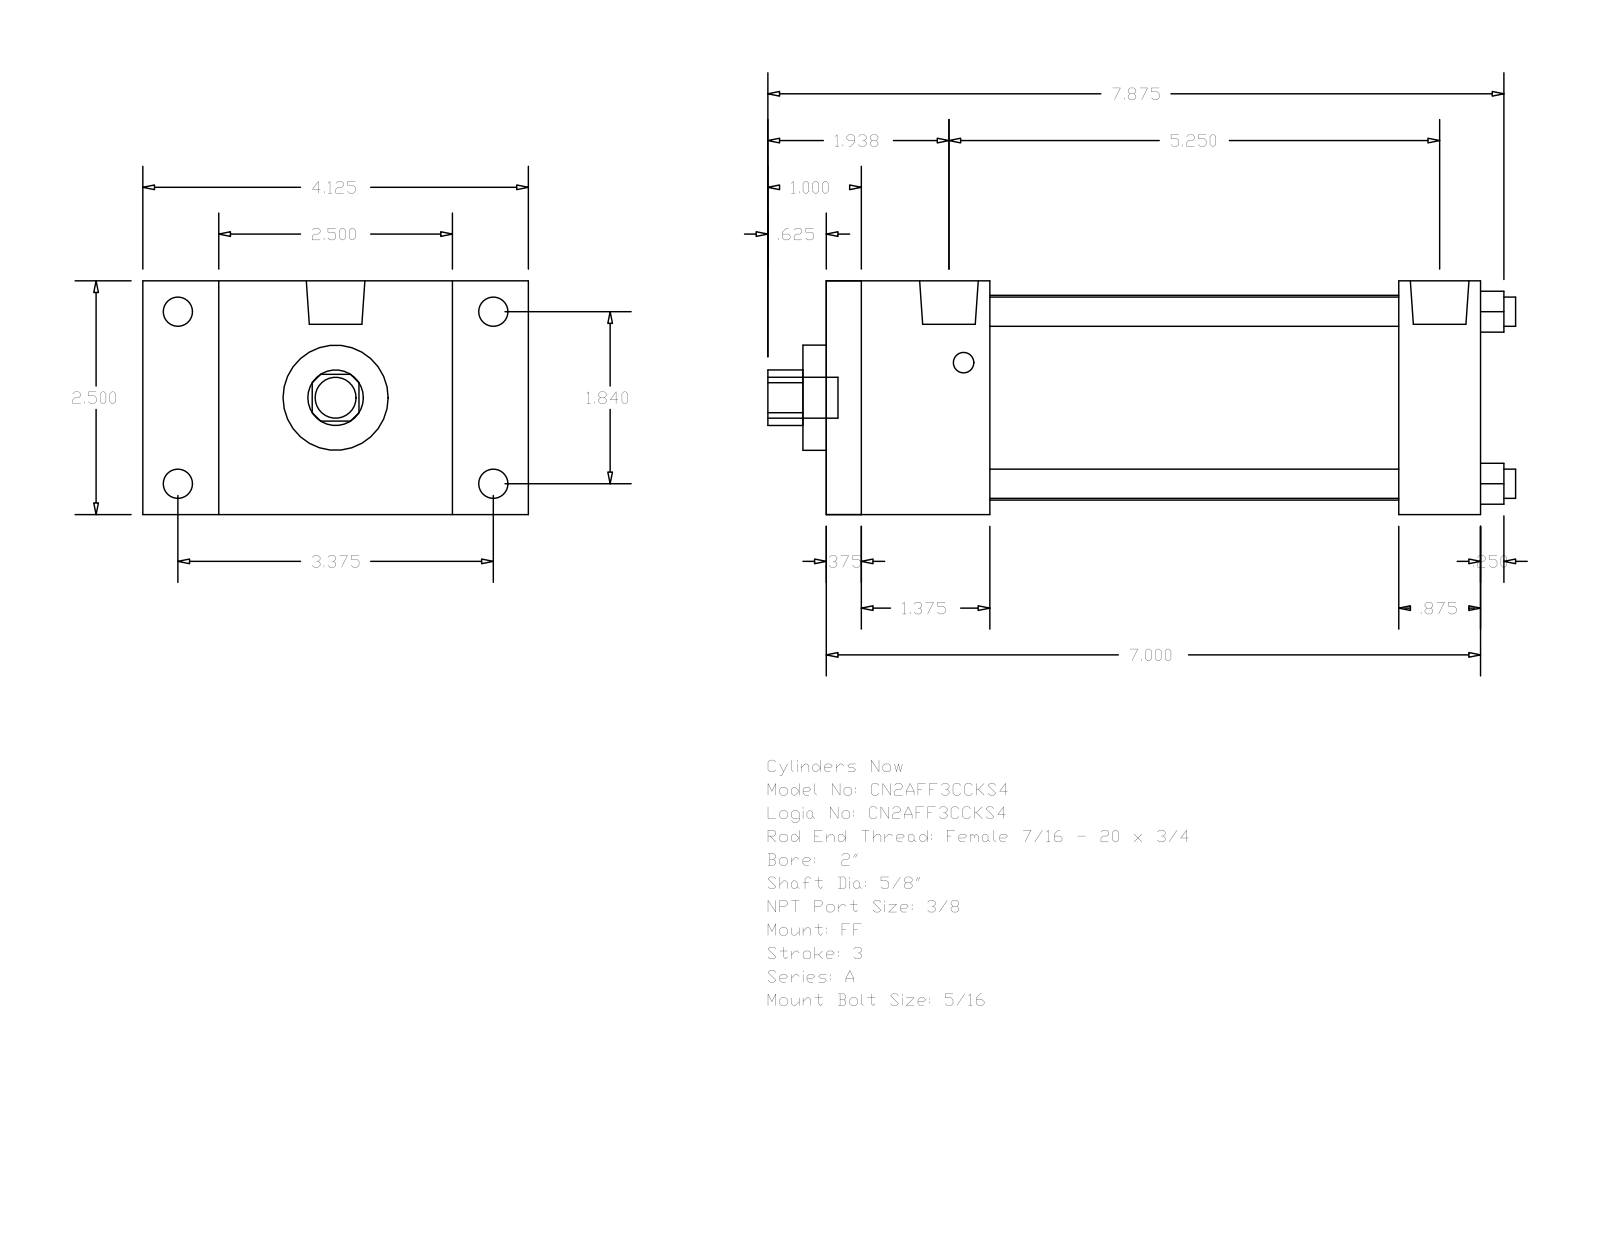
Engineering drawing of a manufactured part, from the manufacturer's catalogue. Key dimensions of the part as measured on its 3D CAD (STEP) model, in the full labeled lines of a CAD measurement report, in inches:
Part name (STEP PRODUCT): A_FF__0200_0.625
STEP written by: GSSL Pune (CONFIG_CONTROL_DESIGN)
Units: inches
Bodies: 0 solids, 92 faces (64 planar, 28 cylindrical, 0 other)
Overall size (bounding box): 8 × 4.125 × 2.5
Round holes (diameter × count): ⌀0.313 ×4, ⌀0.625 ×1, ⌀1.125 ×1, ⌀2.19 ×1
Round bosses / shafts (diameter × count): ⌀0.313 ×4, ⌀0.219 ×4, ⌀0.627 ×2, ⌀0.437 ×1
Partial cylindrical surfaces — rounded edges, fillets, slot ends (radius × count): R0.297 ×1
Main face-to-face distances: 2.5, 7, 0.375, 6.625, 1.75, 6.125, 1.375, 5.75, 4.375, 5.25
Hole centre spacings: 1.301, 1.84, 2.602
